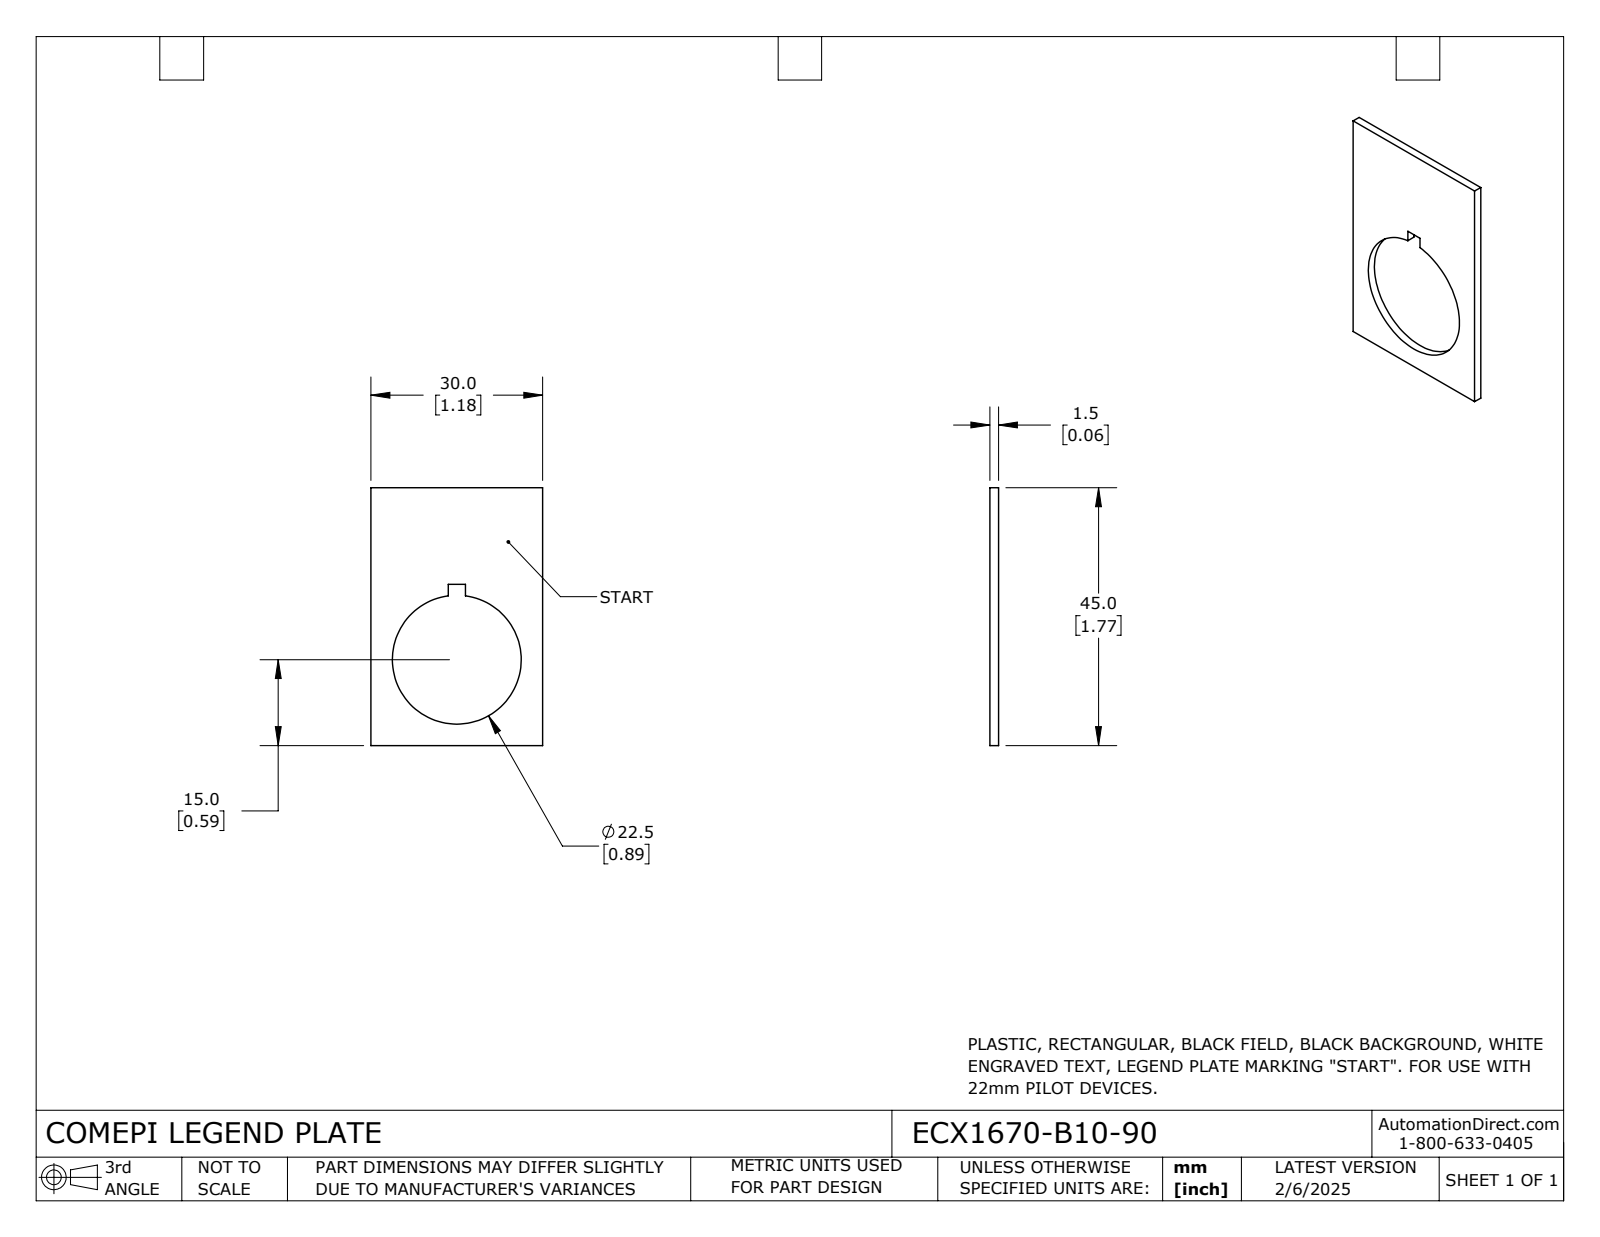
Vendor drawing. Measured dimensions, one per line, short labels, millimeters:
name: ECX1670-B10-90
written by: SolidWorks 2024 (CONFIG_CONTROL_DESIGN)
unit: mm
bodies: 1 solid, 12 faces (9 planar, 3 cylindrical, 0 other)
size: 45 × 30 × 1.5
volume: 1 400 mm³; area: 2 230 mm²
holes: 1× ⌀22.5
face distances: 1.5, 30, 45, 13.5, 16.5, 28.1, 16.8, 3
